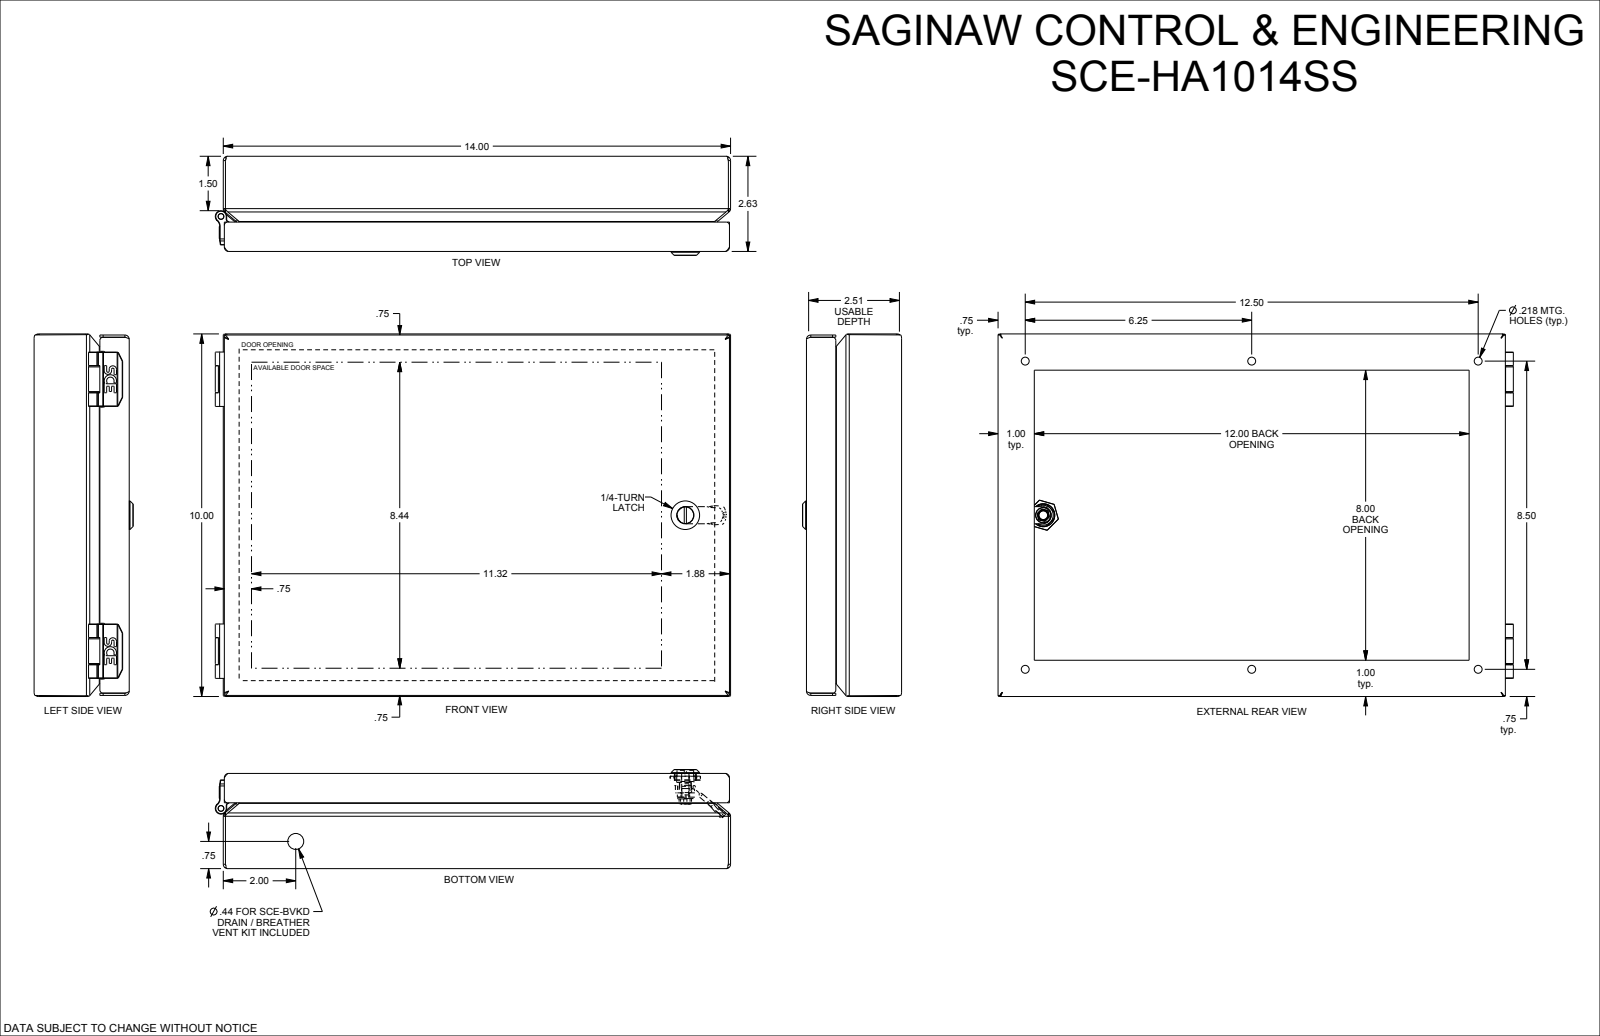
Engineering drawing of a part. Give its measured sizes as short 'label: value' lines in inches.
name: SCE-HA1014
written by: SolidWorks 2021 (AUTOMOTIVE_DESIGN)
unit: in
bodies: 23 solids, 1152 faces (446 planar, 292 cylindrical, 414 other)
size: 14.22 × 10 × 2.732
volume: 23.74 in³; area: 746.1 in²
holes: 6× ⌀0.284, 4× ⌀0.16, 2× ⌀0.02, 2× ⌀0.1, 2× ⌀0.266, 1× ⌀0.158, 1× ⌀0.188, 1× ⌀0.2, 1× ⌀0.239, 1× ⌀0.254, 1× ⌀0.269, 1× ⌀0.282
bosses: 4× ⌀0.483, 4× ⌀0.237, 4× ⌀0.16, 2× ⌀0.26, 2× ⌀0.18, 1× ⌀0.788, 1× ⌀0.548, 1× ⌀0.46
rounds: 28× R0.03, 24× R0.008, 21× R0.013, 16× R0.05, 14× R0.01, 9× R0.02, 8× R0.063, 6× R0.06
face distances: 0.06, 0.059, 2.565, 2.625, 2.506, 2.566, 9.941, 13.941, 10, 9.882
hole spacings: 7.5, 6.25, 10.55, 8.5, 0.017, 4.279, 7.152, 12.5
